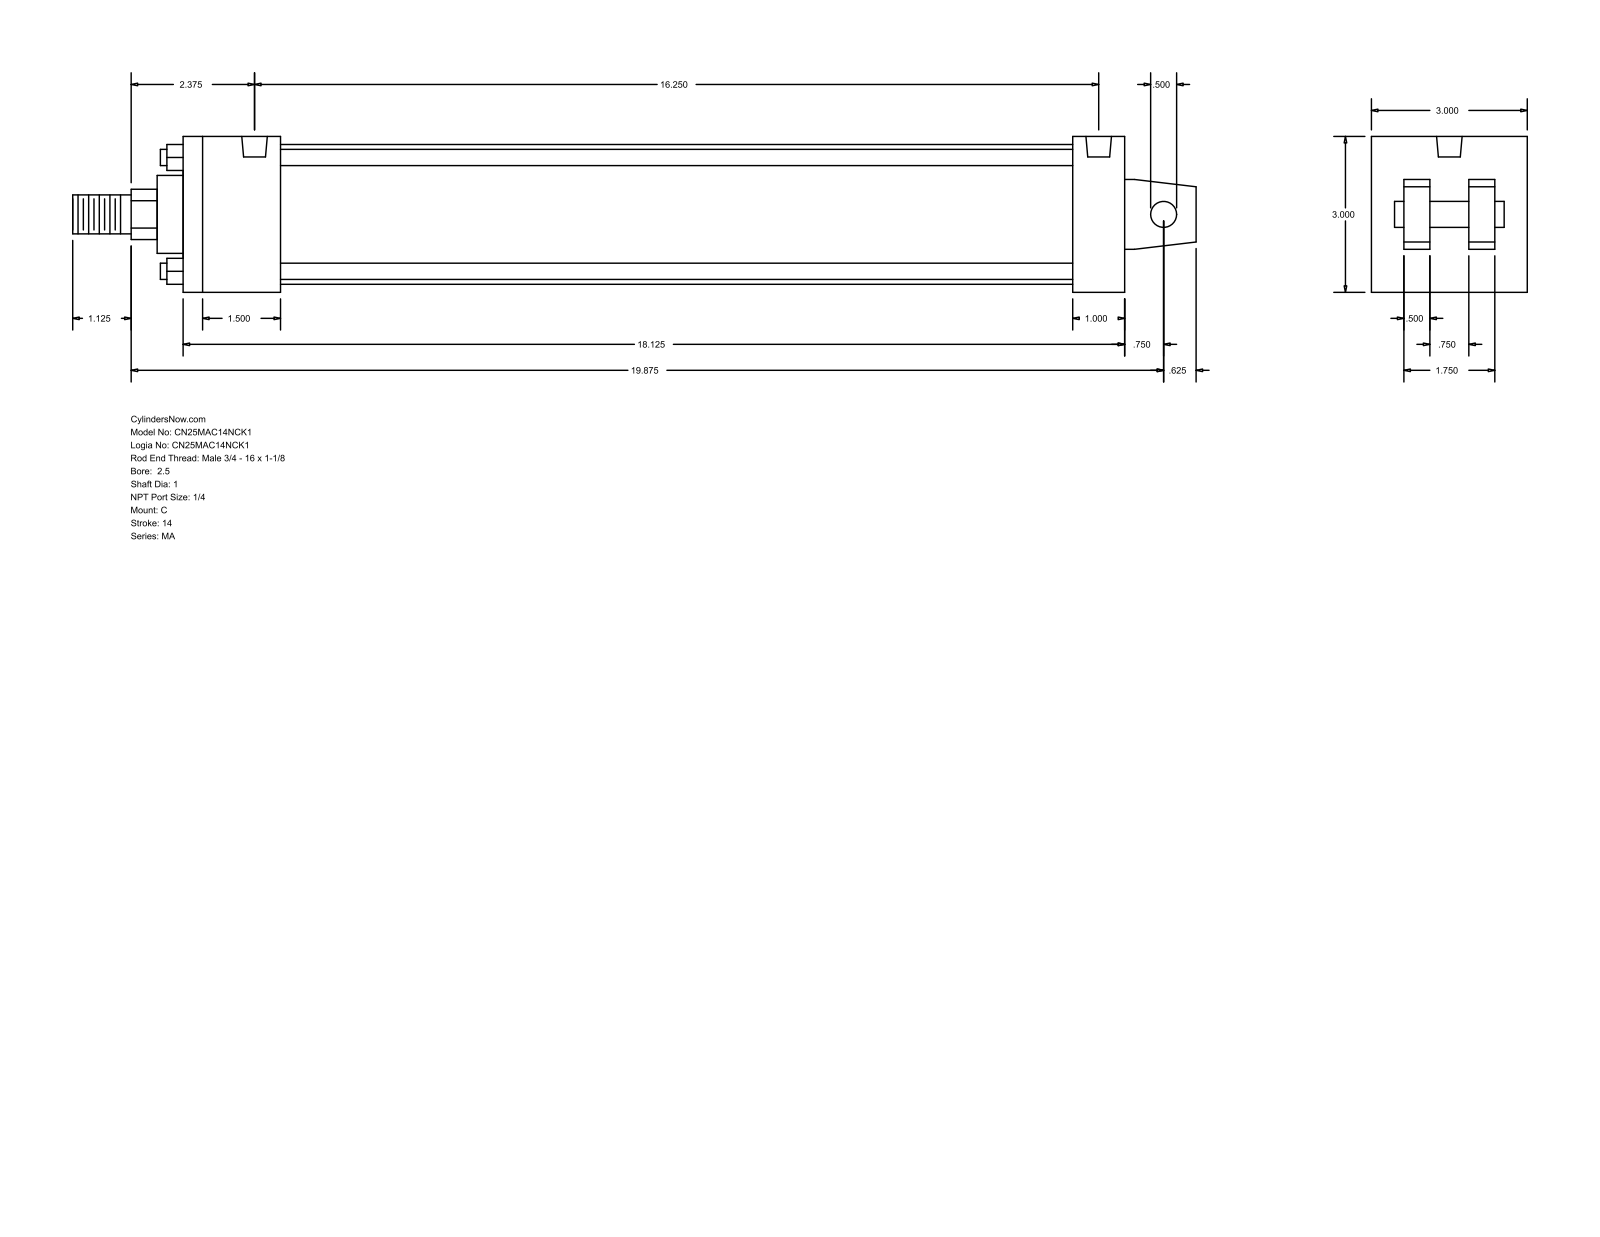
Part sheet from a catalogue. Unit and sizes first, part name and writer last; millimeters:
Units: millimetres
Overall size (bounding box): 549.27 × 76.2 × 76.2
Round holes (diameter × count): ⌀7.94 ×4, ⌀12.49 ×2
Round bosses / shafts (diameter × count): ⌀7.94 ×4, ⌀68.33 ×1, ⌀38.1 ×1, ⌀25.4 ×1, ⌀19.05 ×1, ⌀12.7 ×1
Partial cylindrical surfaces — rounded edges, fillets, slot ends (radius × count): R12.29 ×1
Main face-to-face distances: 76.2, 47.63, 460.37, 12.7, 60.33, 15.87, 28.57, 434.98, 387.35, 412.74
Hole centre spacings: 412.74
Bodies: 0 solids, 103 faces (76 planar, 27 cylindrical, 0 other)
Part name (STEP PRODUCT): MA_C__0250_1
STEP written by: GSSL Pune (CONFIG_CONTROL_DESIGN)
